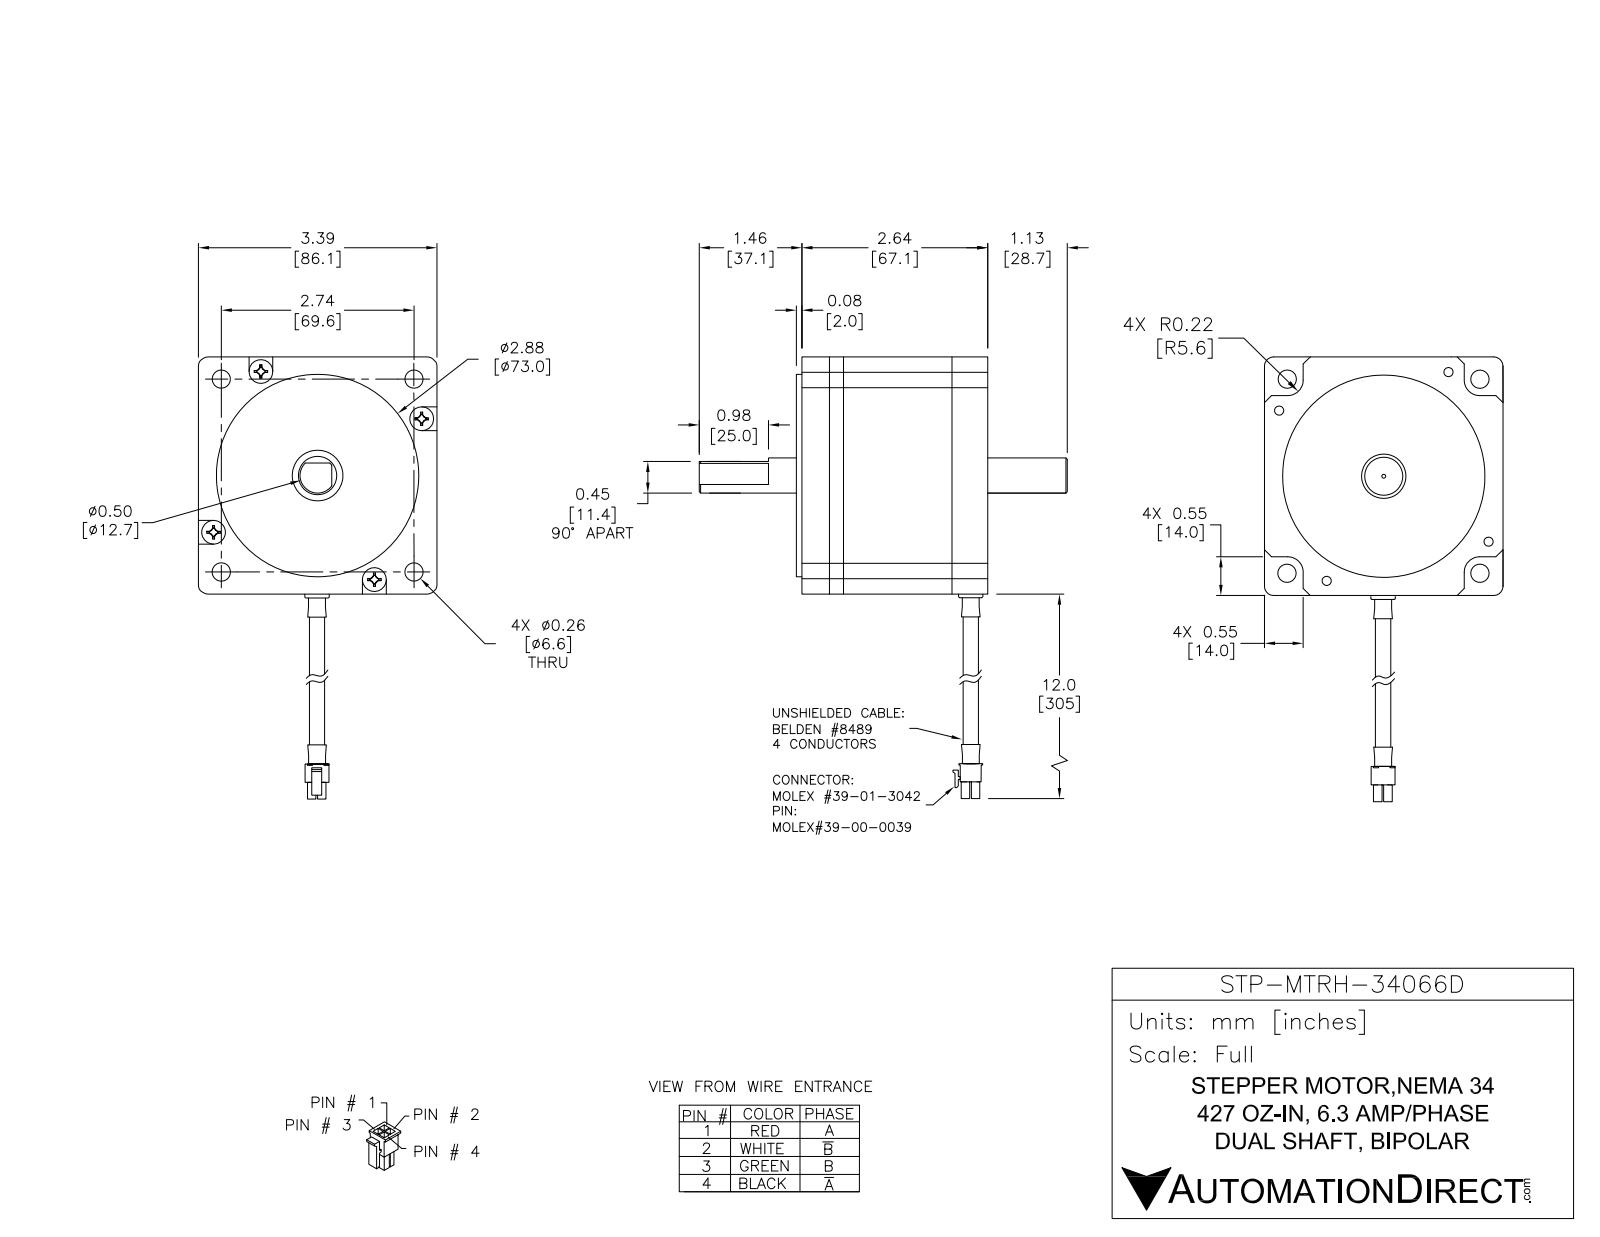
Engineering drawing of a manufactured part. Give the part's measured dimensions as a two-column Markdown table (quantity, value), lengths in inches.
| quantity | value |
| --- | --- |
| part name | 8718S-05PD-13RO Coord fXT |
| STEP written by | SolidWorks 2017 (AUTOMOTIVE_DESIGN) |
| units | inches |
| bodies | 1 solid, 205 faces (107 planar, 71 cylindrical, 27 other) |
| overall size | 5.228 × 4.386 × 3.39 |
| volume | 28.26 in³ |
| surface area | 66.03 in² |
| round holes (diameter × count) | 0.118 × 6, 0.26 × 4, 0.098 × 2, 0.63 × 1, 1.89 × 1, 3.169 × 1 |
| round bosses / shafts (diameter × count) | 0.213 × 4, 2.875 × 1, 1.339 × 1, 0.5 × 1, 0.276 × 1 |
| partial cylindrical surfaces (radius × count) | 0.185 × 8, 0.167 × 4, 0.236 × 4, 0.299 × 4 |
| main face-to-face distances | 3.39, 2.713, 2.634, 0.079, 2.638, 2.717, 0.543, 2.846, 2.579, 2.575 |
| hole center spacings | 0.426, 1.446, 1.791, 1.937, 2.121, 2.341, 2.533, 2.657 |
